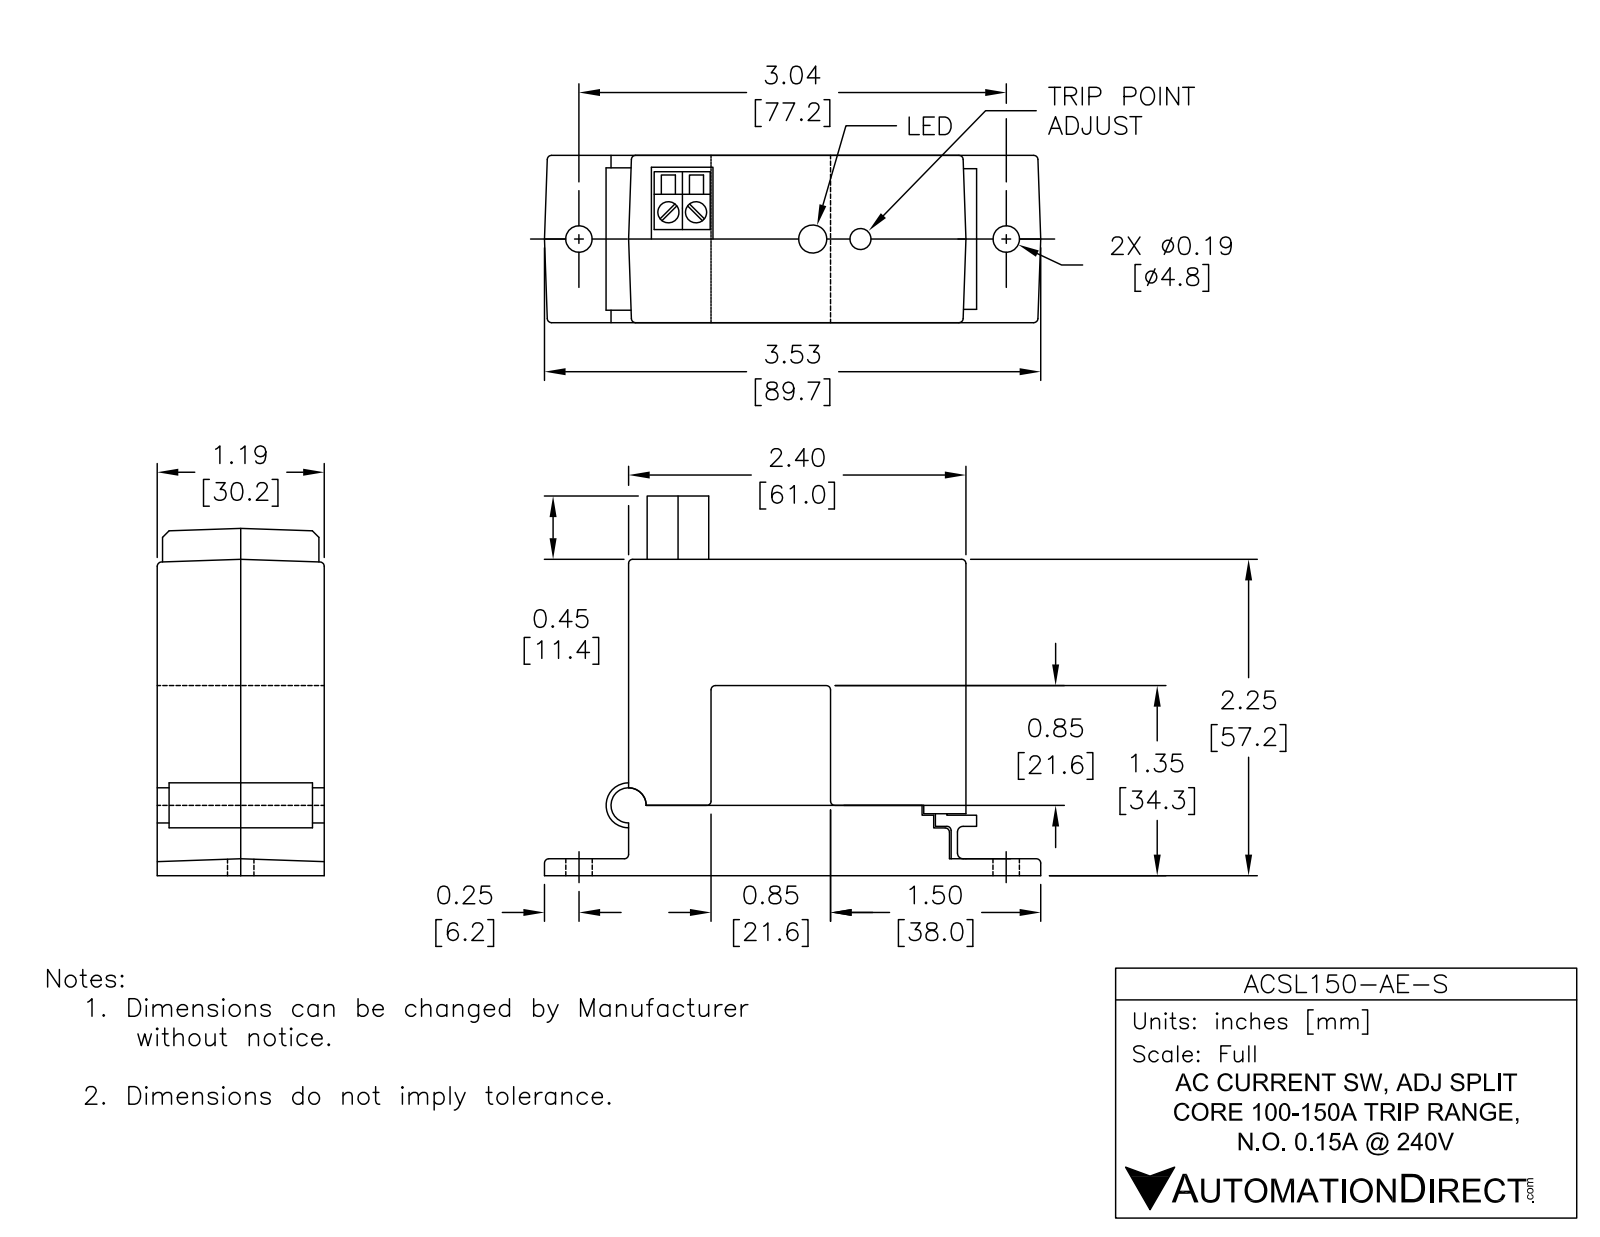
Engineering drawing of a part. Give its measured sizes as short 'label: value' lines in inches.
name: ACSL150-AE-S
written by: SolidWorks 2018 (AUTOMOTIVE_DESIGN)
unit: in
bodies: 8 solids, 475 faces (323 planar, 138 cylindrical, 14 other)
size: 3.53 × 2.743 × 1.2
volume: 5.749 in³; area: 53.51 in²
holes: 2× ⌀0.158, 2× ⌀0.188, 2× ⌀0.2, 1× ⌀0.18
bosses: 2× ⌀0.154, 1× ⌀0.3, 1× ⌀0.25, 1× ⌀0.187, 1× ⌀0.135, 1× ⌀0.063
rounds: 27× R0.016, 2× R0.014, 1× R0.089
face distances: 0.6, 2.258, 1.2, 0.605, 0.595, 0.508, 1.75, 1.75, 2.258, 2.4
hole spacings: 0.171, 0.345, 0.606, 0.772, 0.835, 1.002, 1.102, 1.174
